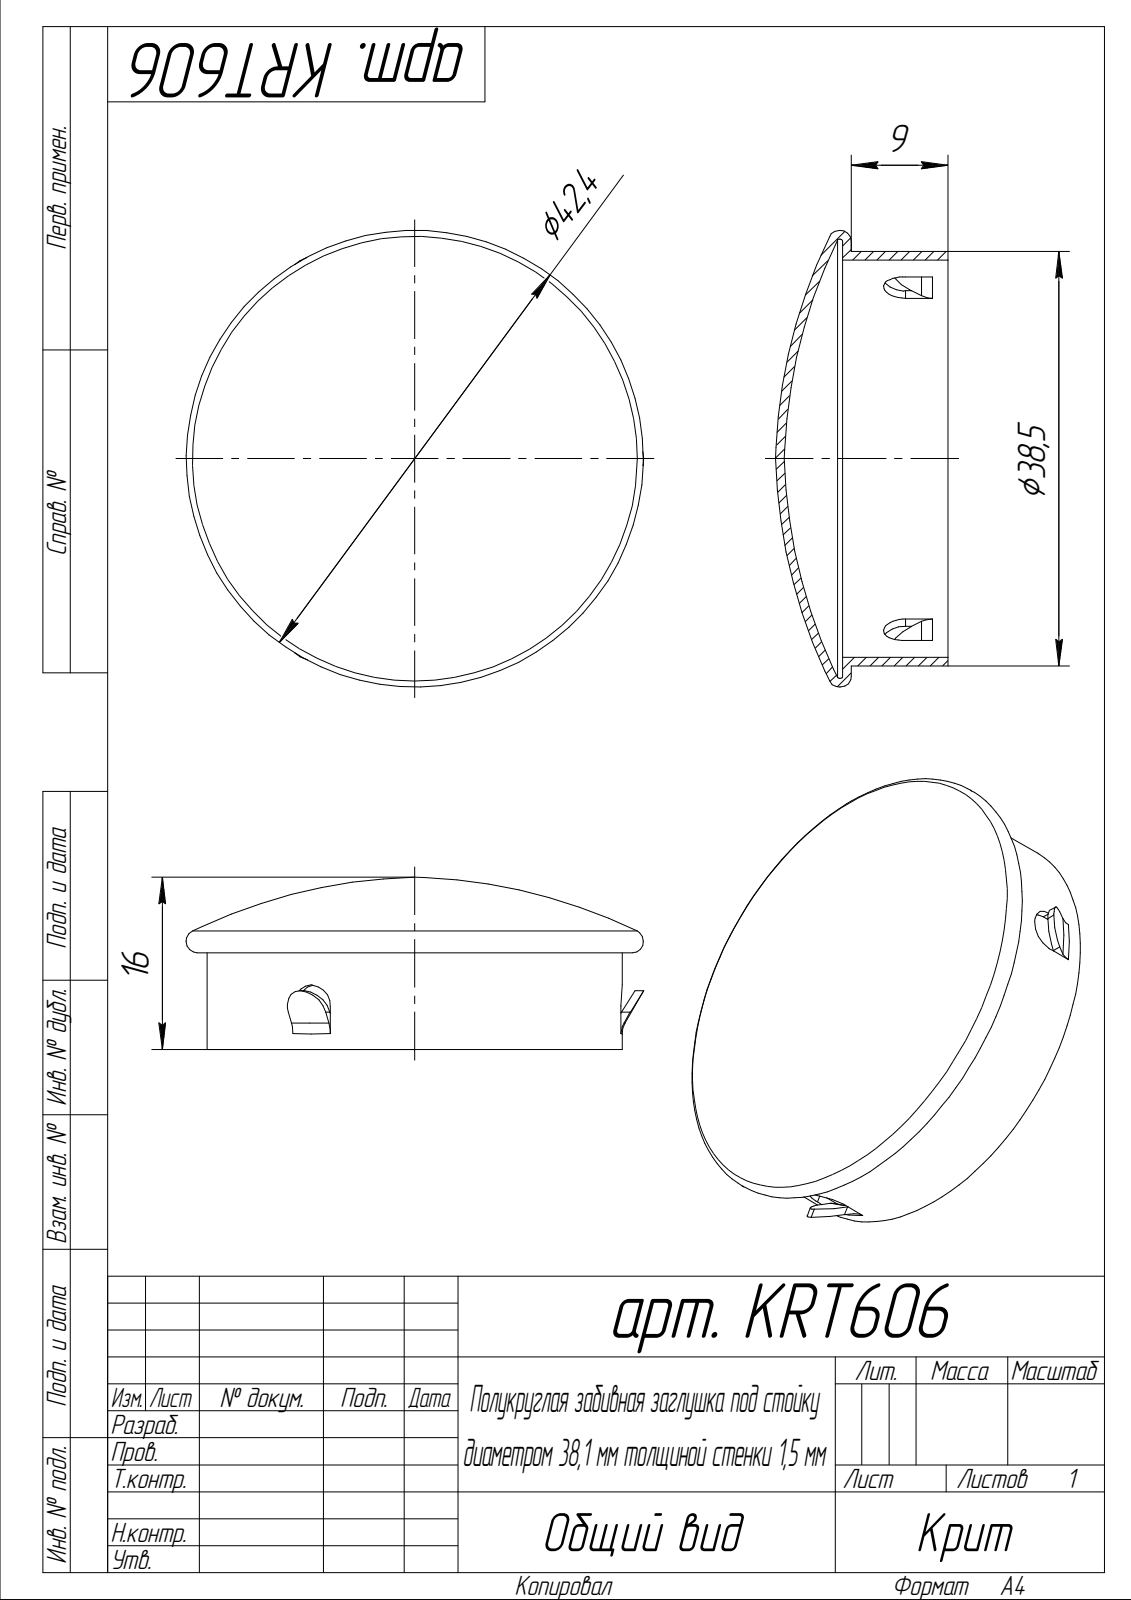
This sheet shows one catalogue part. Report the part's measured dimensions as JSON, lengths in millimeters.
{"part_name": "арт. KRT606", "step_written_by": "SolidWorks 2014 (AUTOMOTIVE_DESIGN)", "units": "millimeters", "bodies": {"solids": 1, "faces": 59, "planar": 15, "cylindrical": 20, "other": 24}, "overall_size": [42.45, 42.4, 16], "volume_mm3": 2306, "surface_area_mm2": 5912, "round_holes": [[36.9, 1], [40.8, 1]], "round_bosses_or_shafts": [[42.4, 1], [38.5, 1]], "partial_cylinders_radius": [[2.03, 6], [2, 3]], "face_to_face_distances": [0.8, 9, 9.8, 4]}
